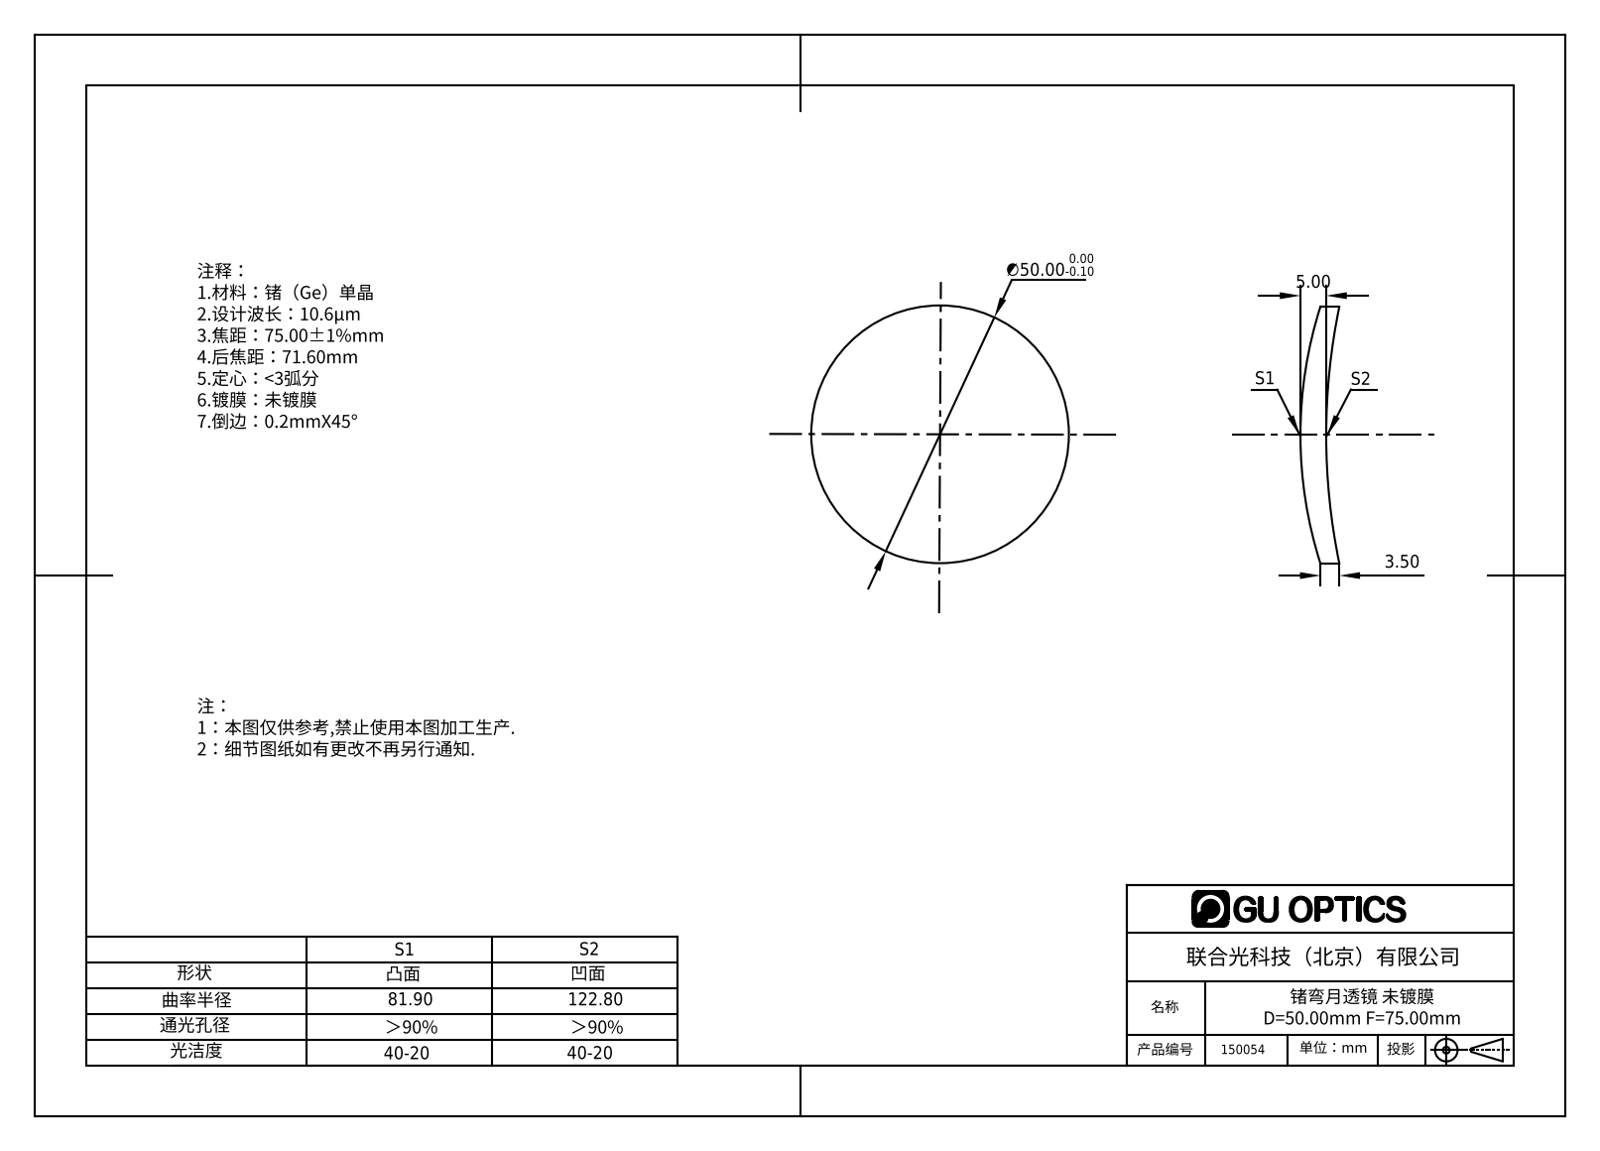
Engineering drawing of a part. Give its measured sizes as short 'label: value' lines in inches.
name: 150054
written by: SolidWorks 2016 (AUTOMOTIVE_DESIGN)
unit: in
bodies: 1 solid, 6 faces (0 planar, 2 cylindrical, 4 other)
size: 1.969 × 1.969 × 0.298
volume: 0.52 in³; area: 7.085 in²
bosses: 1× ⌀1.969
